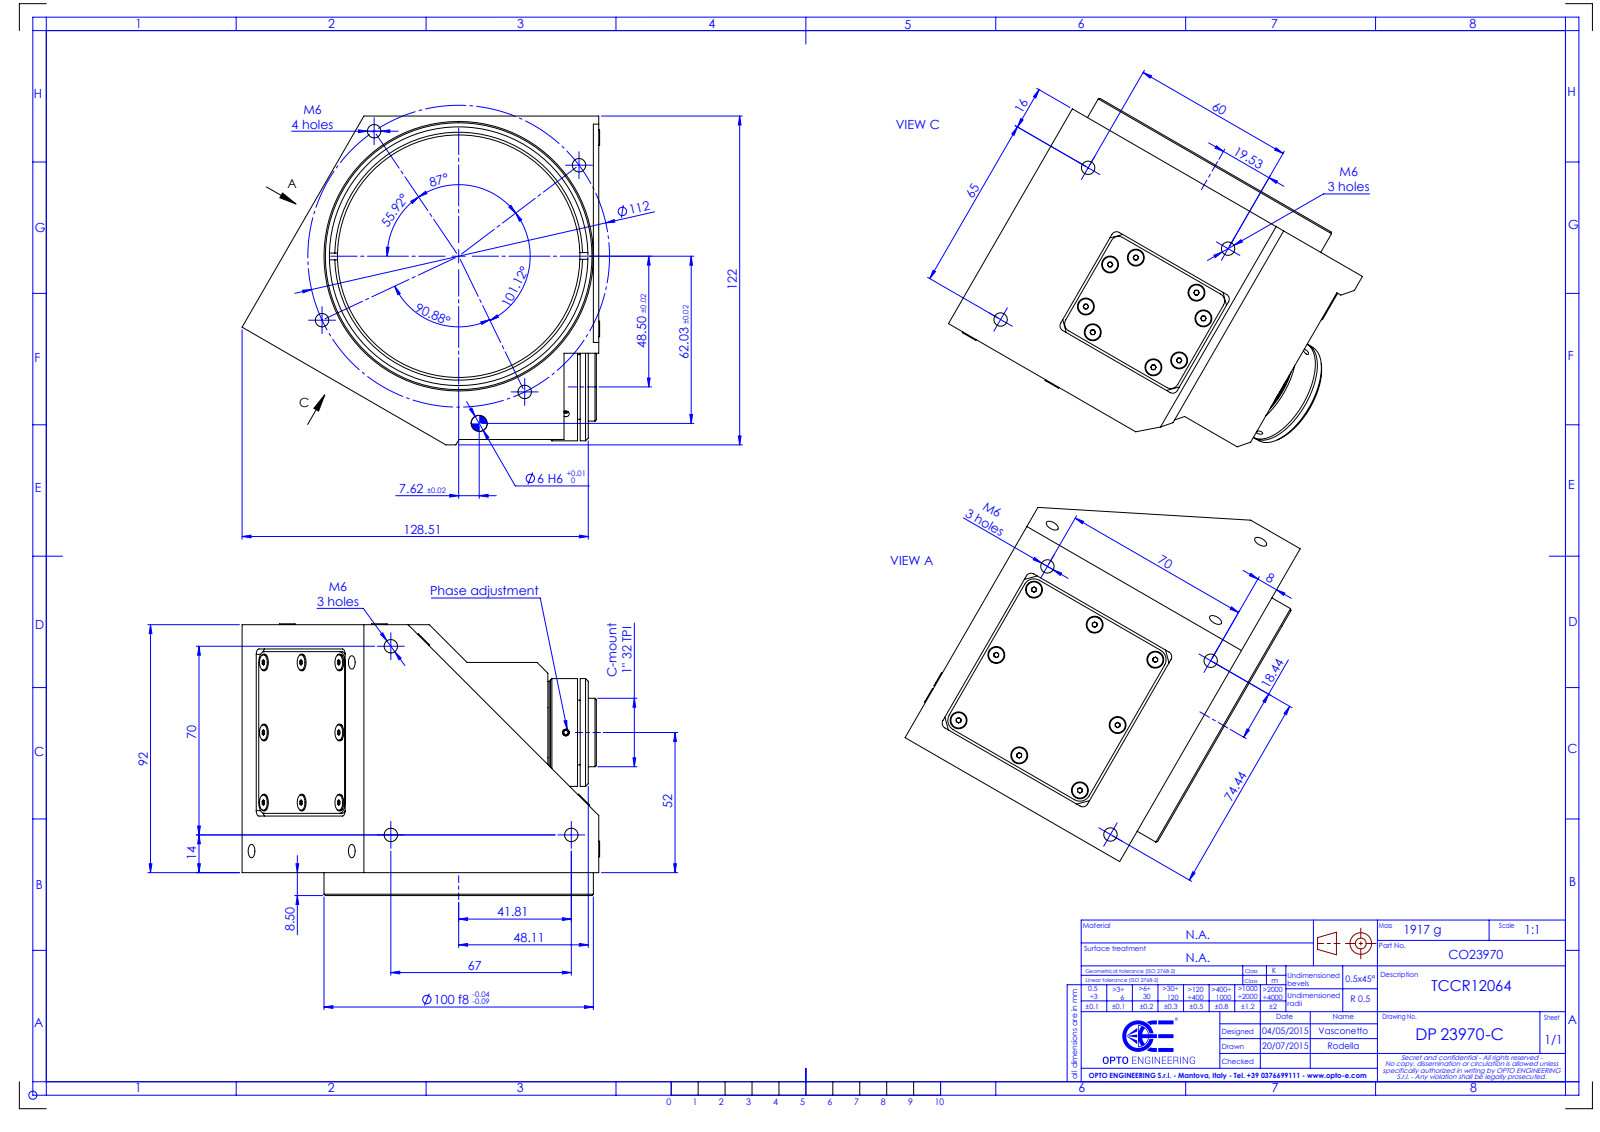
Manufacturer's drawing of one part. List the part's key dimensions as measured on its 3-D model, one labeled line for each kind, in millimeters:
Part name (STEP PRODUCT): DP23970_TCCR12064
STEP written by: SolidWorks 2021 (CONFIG_CONTROL_DESIGN)
Units: millimetres
Bodies: 0 solids, 407 faces (183 planar, 118 cylindrical, 106 other)
Overall size (bounding box): 132.73 × 122 × 100.83
Round holes (diameter × count): ⌀5 ×13, ⌀2.5 ×3, ⌀6 ×1, ⌀14.5 ×1, ⌀22 ×1, ⌀22.5 ×1, ⌀90 ×1, ⌀96 ×1
Round bosses / shafts (diameter × count): ⌀5.75 ×22, ⌀100 ×1, ⌀40 ×1, ⌀38.2 ×1, ⌀37.8 ×1, ⌀25.4 ×1
Partial cylindrical surfaces — rounded edges, fillets, slot ends (radius × count): R2 ×8, R4 ×6, R3 ×4
Main face-to-face distances: 0.5, 92, 120, 1, 36, 18.89, 84, 3, 10, 4
Hole centre spacings: 56, 70, 20.54, 38.05, 60, 62.5, 65, 67
